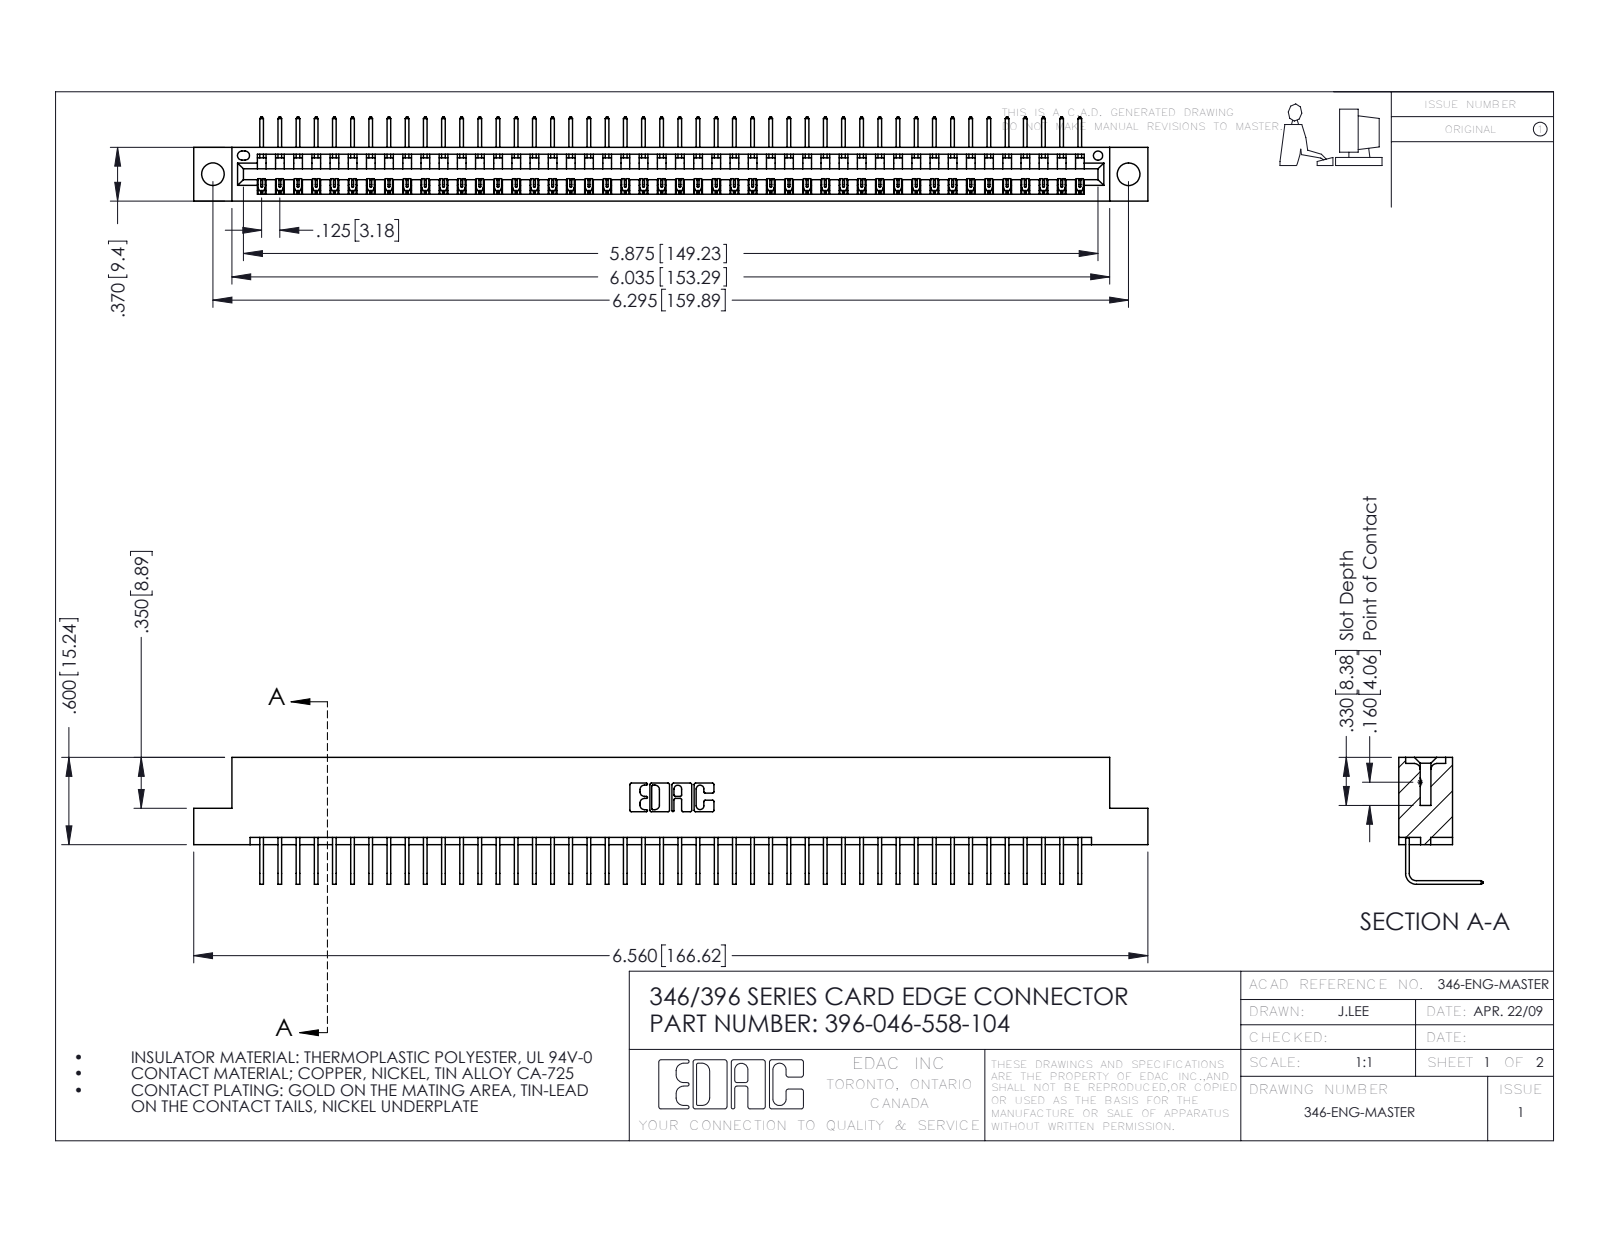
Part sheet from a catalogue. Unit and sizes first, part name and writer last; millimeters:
Units: millimetres
Overall size (bounding box): 166.6 × 22.2 × 14.7
Round holes (diameter × count): ⌀4 ×2, ⌀1.6 ×1
Partial cylindrical surfaces — rounded edges, fillets, slot ends (radius × count): R0.2 ×92, R0.3 ×22, R0.2 ×6, R0.8 ×6, R0.7 ×3, R0.8 ×2, R1 ×2, R0.4 ×1
Main face-to-face distances: 8.2, 1.2, 9.4, 6.4, 7.6, 0.6, 1.8, 3.8, 5.6, 2.5
Hole centre spacings: 6.2, 154.6, 159.9
Volume: 16 000 mm³ · Surface area: 20 810 mm²
Bodies: 47 solids, 2882 faces (2008 planar, 874 cylindrical, 0 other)
Part name (STEP PRODUCT): 396-046-558-104; 345-292-001_558 Tail - 2; 346 Part_Flush Mounting Lugs - 0.156 Dia-TH
STEP written by: SolidWorks 2016 (CONFIG_CONTROL_DESIGN)
